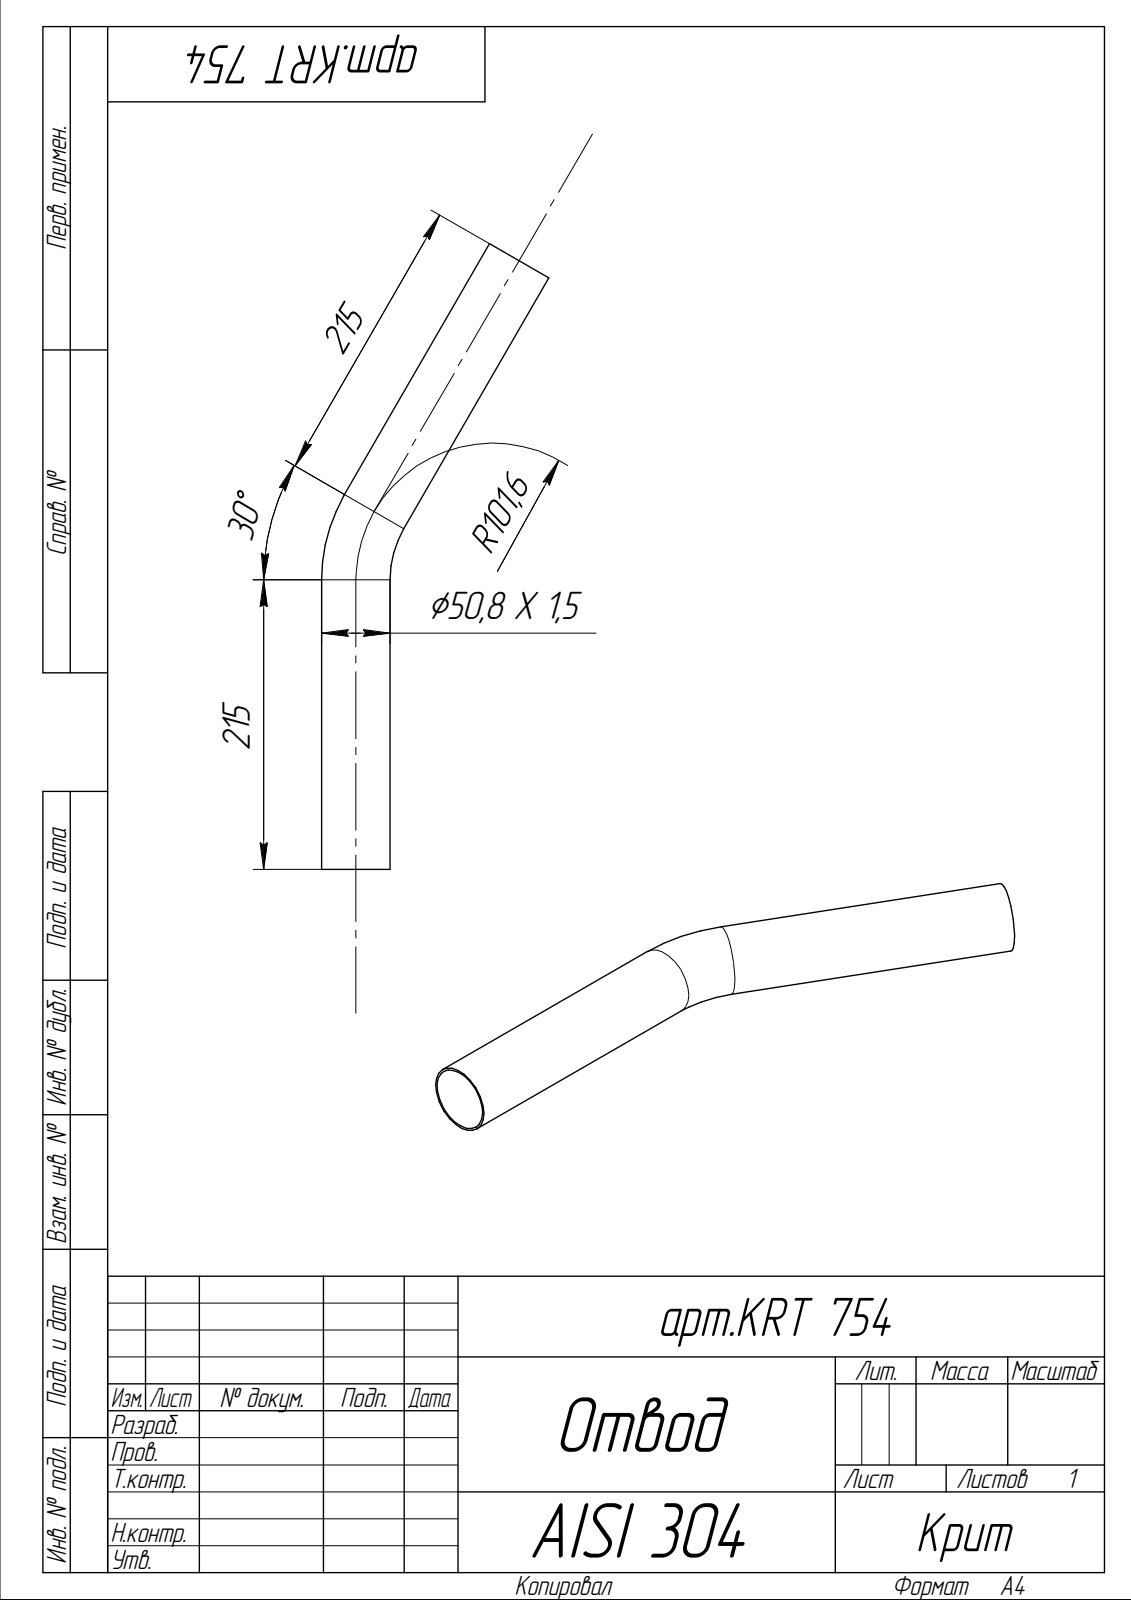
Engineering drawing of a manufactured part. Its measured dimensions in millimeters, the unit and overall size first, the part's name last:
Units: millimetres
Overall size (bounding box): 464.69 × 168.51 × 50.8
Round holes (diameter × count): ⌀47.8 ×2
Round bosses / shafts (diameter × count): ⌀50.8 ×2
Volume: 112 257 mm³ · Surface area: 150 140 mm²
Bodies: 1 solid, 8 faces (2 planar, 4 cylindrical, 2 other)
Part name (STEP PRODUCT): Деталь
STEP written by: ASCON Math Kernel (AUTOMOTIVE_DESIGN)
